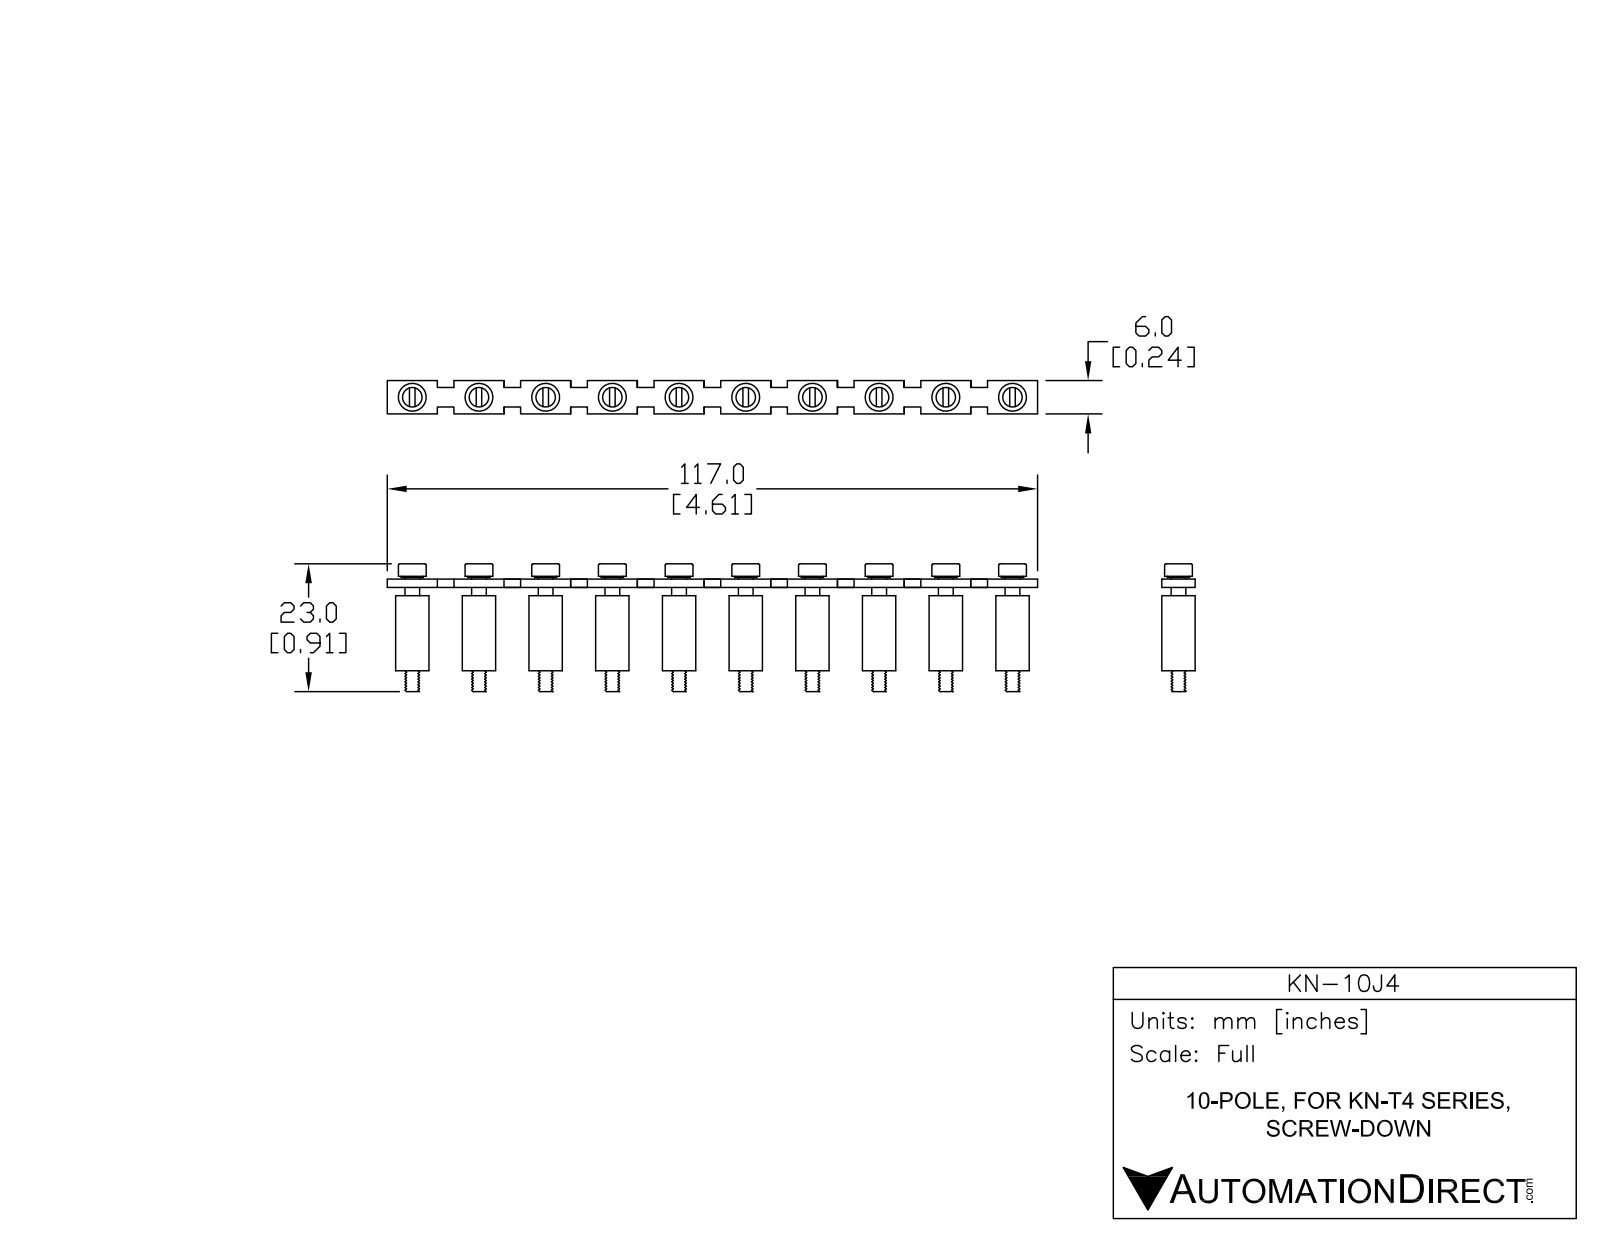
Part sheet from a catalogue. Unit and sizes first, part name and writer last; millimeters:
Units: millimetres
Overall size (bounding box): 117 × 23 × 6
Round holes (diameter × count): ⌀3.15 ×10, ⌀3.5 ×10
Round bosses / shafts (diameter × count): ⌀6 ×10, ⌀5 ×10, ⌀4 ×10, ⌀2.65 ×10
Main face-to-face distances: 1.5, 13.5, 15, 16.5, 3, 2, 0.5, 1.75, 2.25, 3.5
Hole centre spacings: 12, 24, 36, 48, 60, 72, 84, 96
Volume: 4 776 mm³ · Surface area: 9 398 mm²
Bodies: 31 solids, 418 faces (208 planar, 150 cylindrical, 60 other)
Part name (STEP PRODUCT): KN-10J4
STEP written by: SolidWorks 2014 (AUTOMOTIVE_DESIGN)
